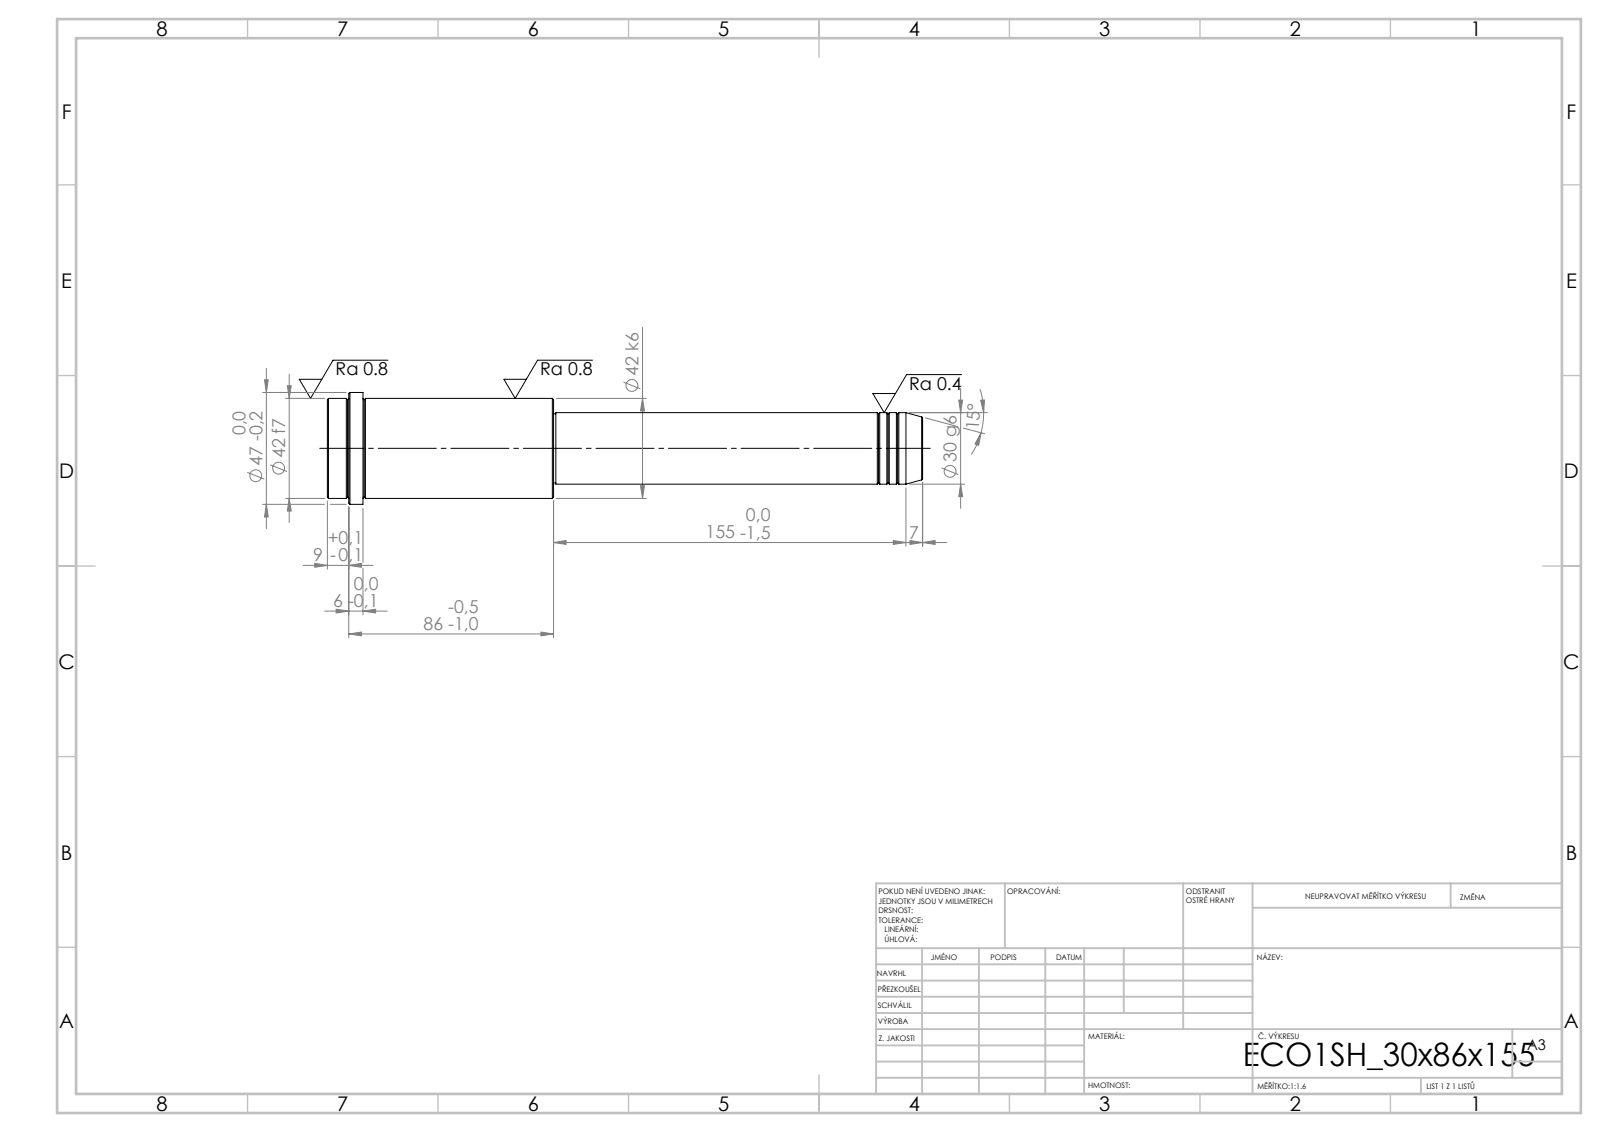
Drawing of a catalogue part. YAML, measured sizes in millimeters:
step_written_by: "SolidWorks 2019 (CONFIG_CONTROL_DESIGN)"
units: millimeters
bodies: {solids: 1, faces: 52, planar: 6, cylindrical: 16, other: 30}
overall_size: [250, 47, 47]
volume: 242372
surface_area: 30777
round_bosses_or_shafts:
  - {diameter: 47, count: 1}
  - {diameter: 42, count: 1}
  - {diameter: 30, count: 1}
  - {diameter: 29, count: 1}
face_to_face_distances: [95, 155, 250, 235, 80, 15, 241, 86, 6, 9]
